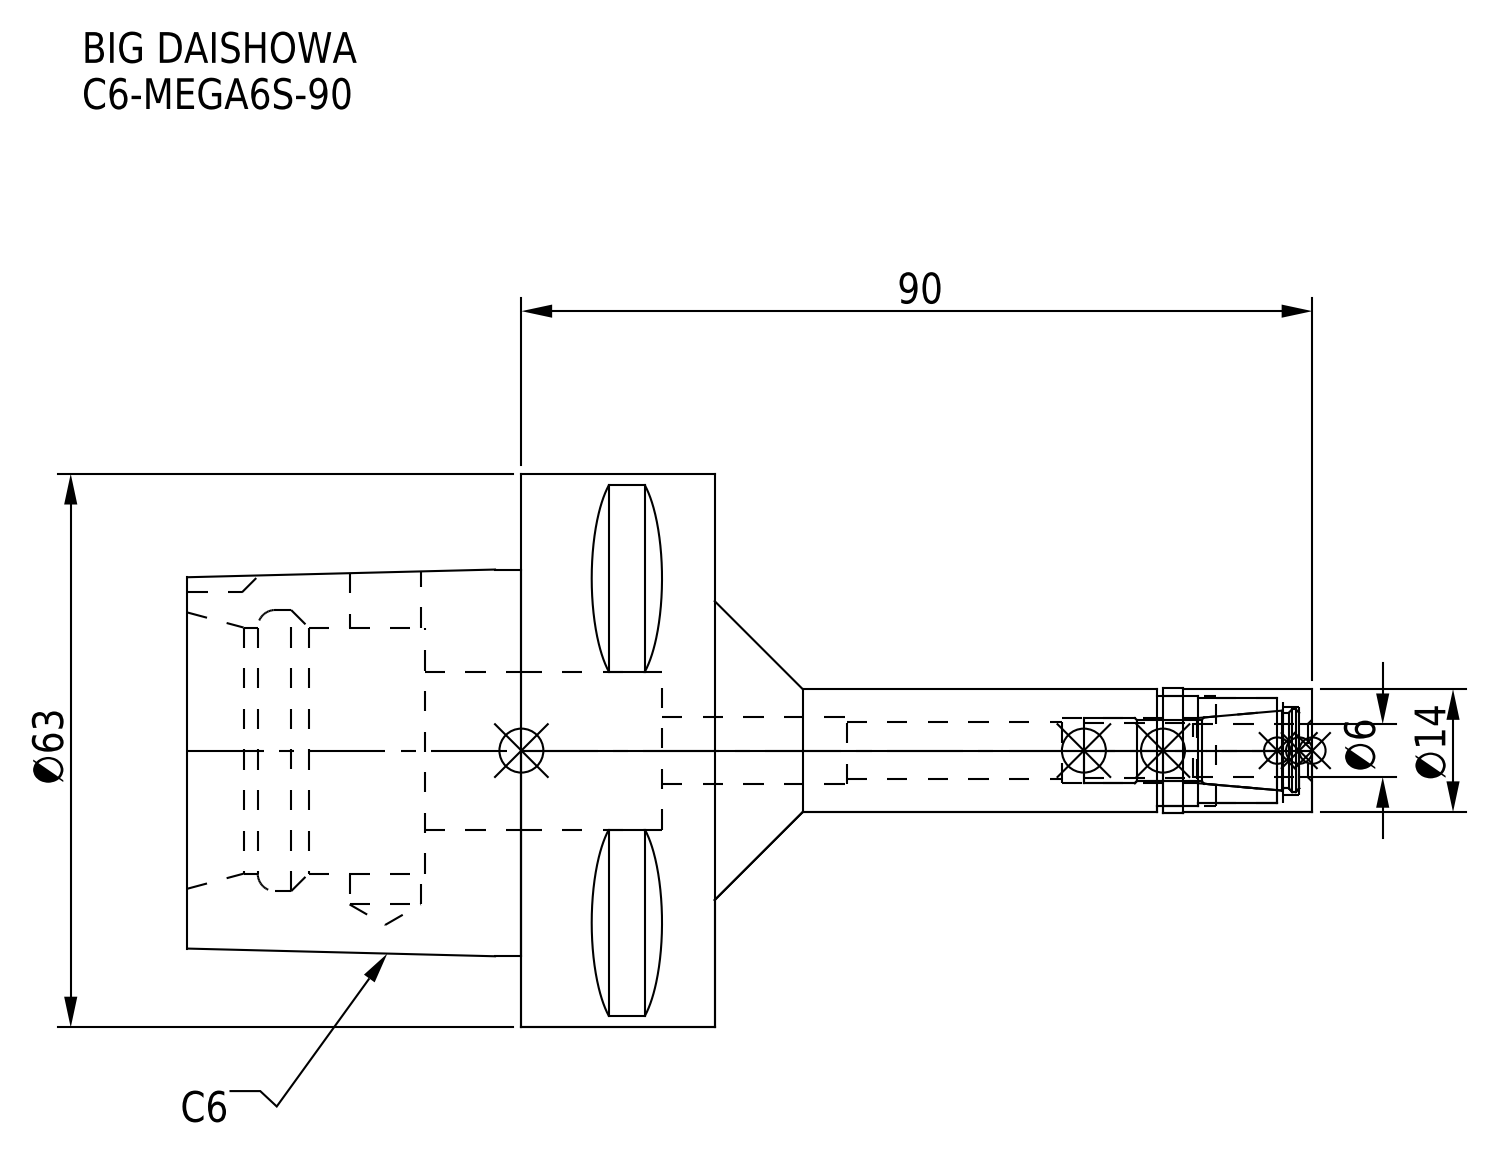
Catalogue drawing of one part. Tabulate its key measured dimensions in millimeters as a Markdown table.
| quantity | value |
| --- | --- |
| part name | DXF_TEMP_ASSY_ASM_4_ASM.stp; C6-MEGA6S-90-060-FreeParts; C6-MEGA6S-90-060.stp; C6-MEGA6S-90 (+3 more) |
| STEP written by | SolidWorks 2019 (CONFIG_CONTROL_DESIGN) |
| units | millimeters |
| bodies | 2 solids, 93 faces (38 planar, 39 cylindrical, 16 other) |
| overall size | 128 × 63 × 63 |
| volume | 107 120 mm³ |
| surface area | 25 871 mm² |
| round holes (diameter × count) | 6.1 × 1, 6.4 × 1, 7.4 × 1, 7.6 × 1, 8.1 × 1, 10 × 1, 12 × 1, 12.5 × 1, 18 × 1, 28 × 1, 32 × 1 |
| round bosses / shafts (diameter × count) | 63 × 1, 14.3 × 1, 14 × 1 |
| partial cylindrical surfaces (radius × count) | 5 × 1 |
| main face-to-face distances | 22, 27, 60, 38, 11, 33, 24.89, 55.4, 6, 16 |
